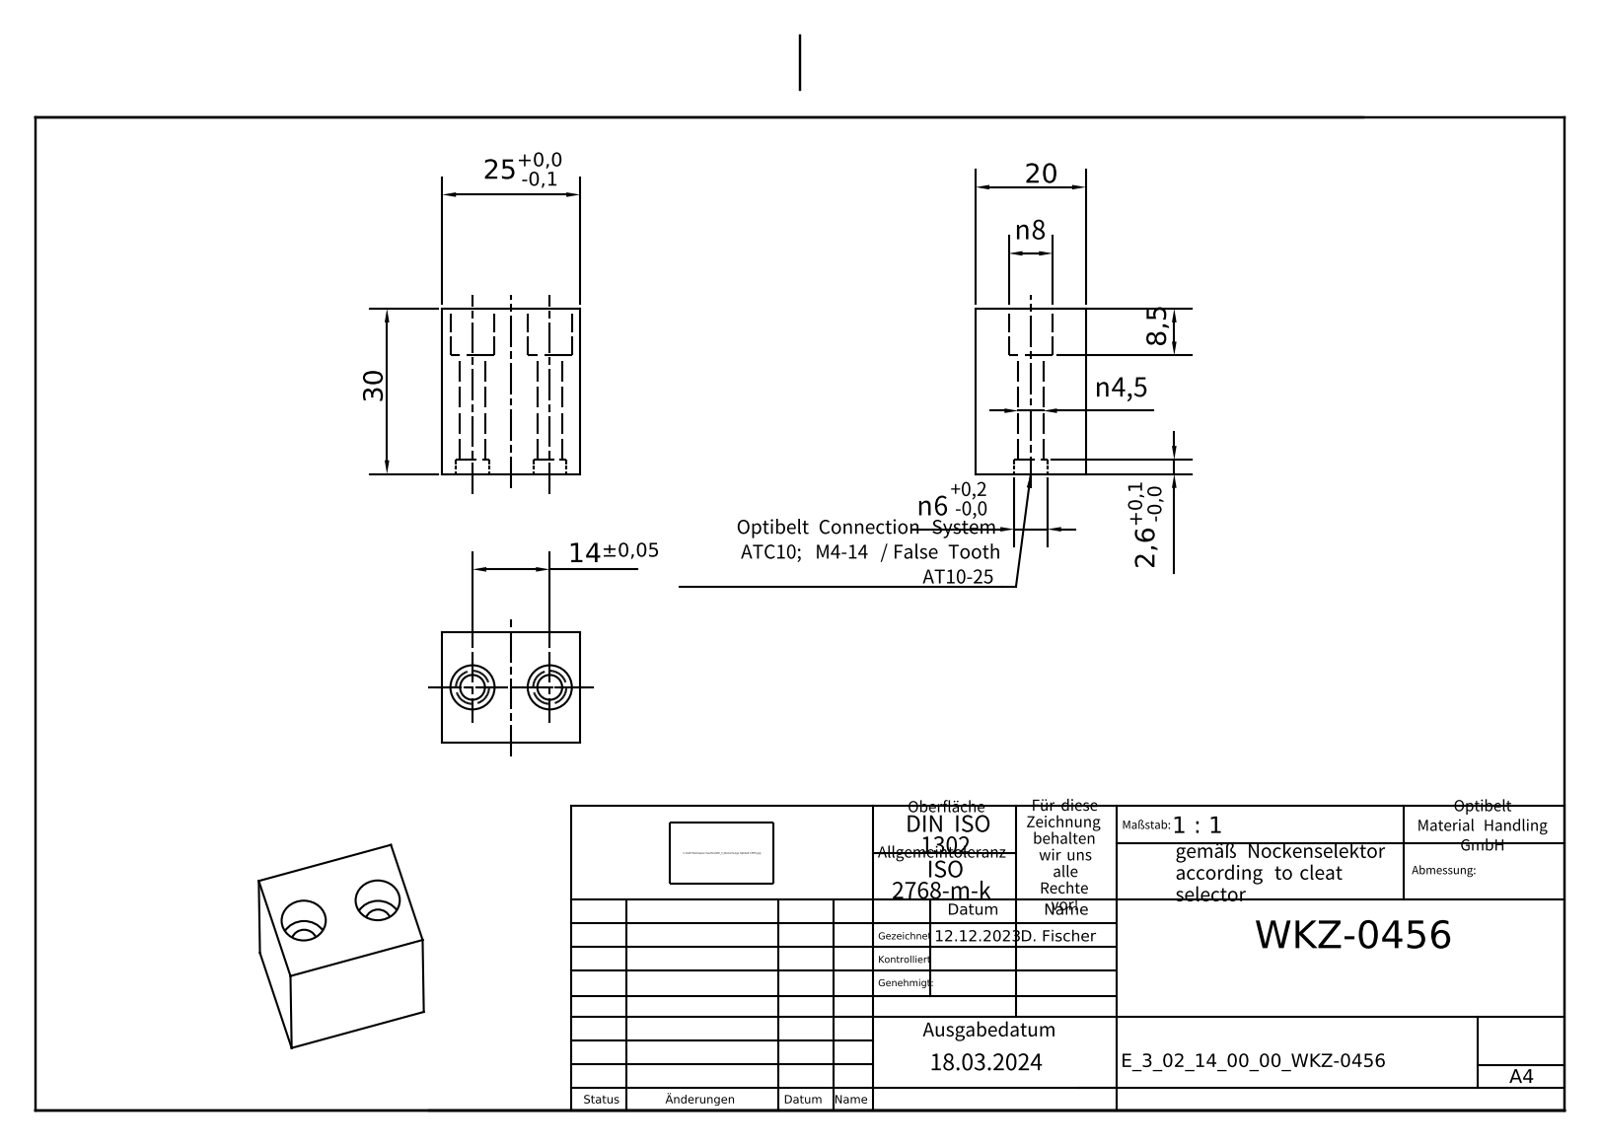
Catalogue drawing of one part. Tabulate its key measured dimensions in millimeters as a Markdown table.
| quantity | value |
| --- | --- |
| part name | E_3_02_14_00_00_WKZ-0456 |
| STEP written by | Autodesk Inventor 2025 (AUTOMOTIVE_DESIGN) |
| units | millimeters |
| bodies | 1 solid, 16 faces (10 planar, 6 cylindrical, 0 other) |
| overall size | 30 × 25 × 20 |
| volume | 13 397 mm³ |
| surface area | 4 696 mm² |
| round holes (diameter × count) | 4.5 × 2, 6 × 2, 8 × 2 |
| main face-to-face distances | 20, 25, 30, 21.5, 8.5, 2.6, 18.9, 27.4 |
| hole center spacings | 14 |
